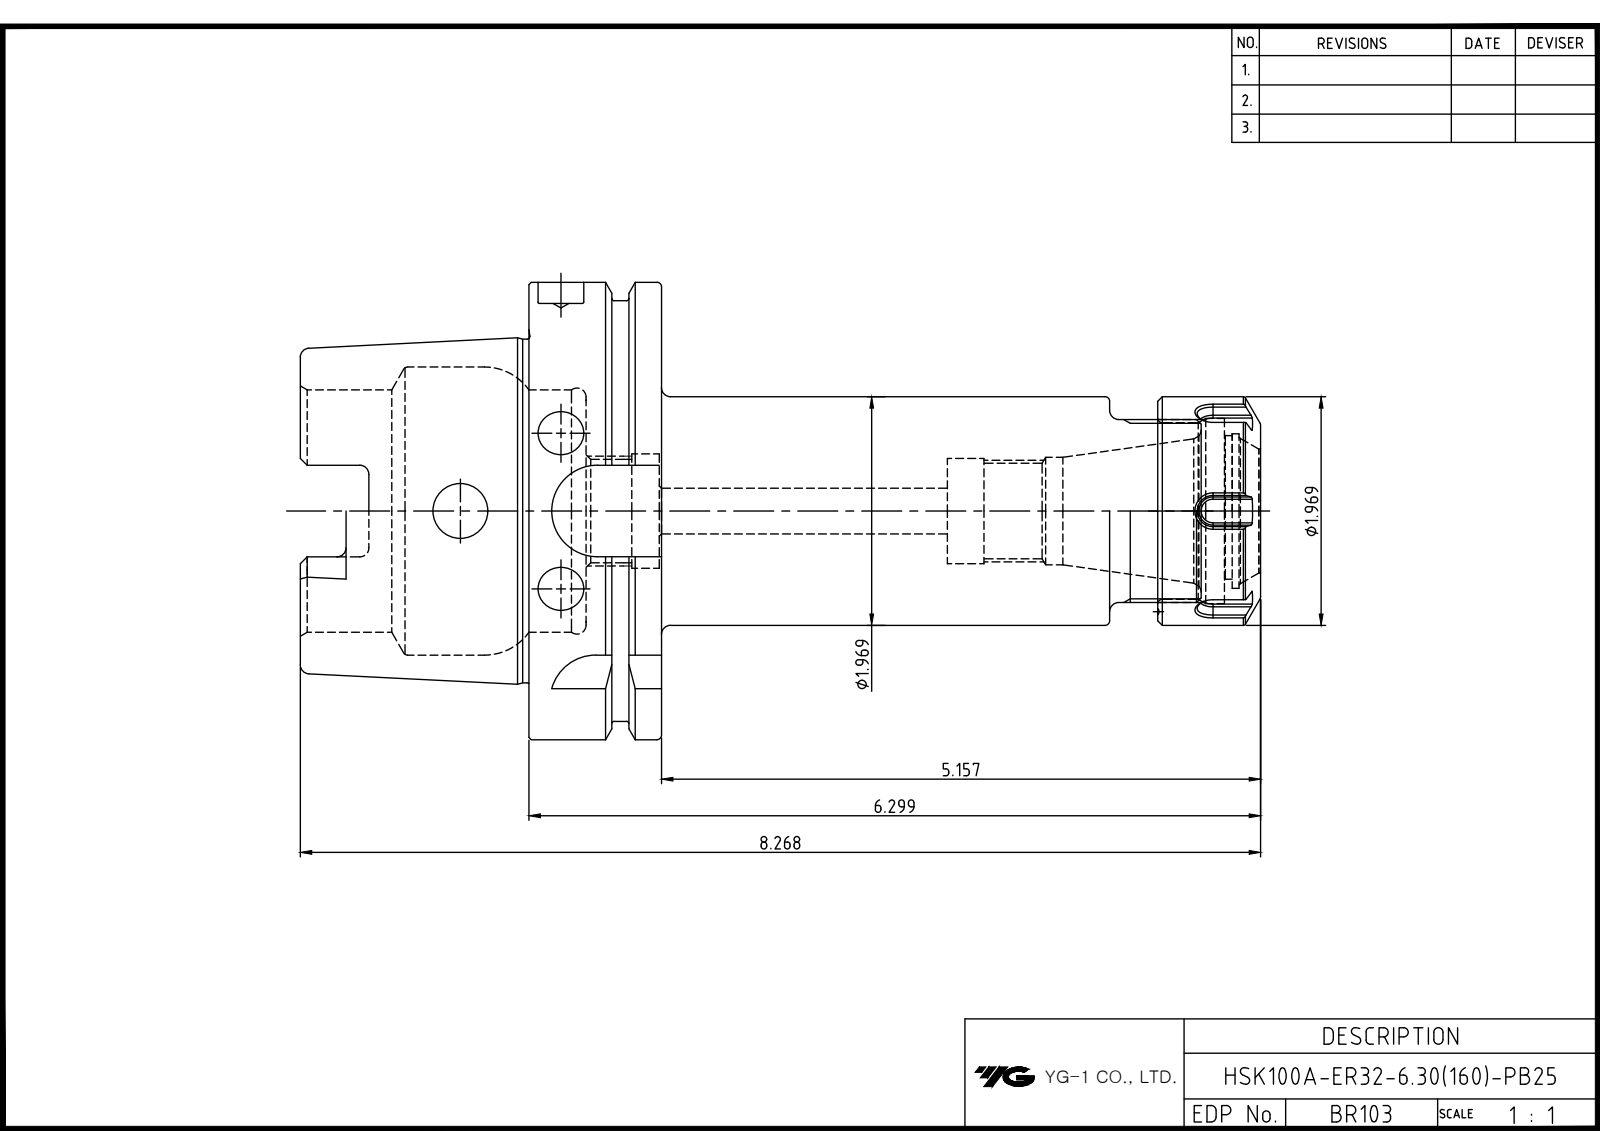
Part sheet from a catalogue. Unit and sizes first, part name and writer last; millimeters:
Units: millimetres
Overall size (bounding box): 210 × 100 × 100
Round holes (diameter × count): ⌀10 ×2, ⌀1 ×1, ⌀12 ×1, ⌀20.5 ×1, ⌀22.38 ×1, ⌀23 ×1, ⌀23.5 ×1, ⌀25 ×1, ⌀27.1 ×1, ⌀31.4 ×1, ⌀33.8 ×1, ⌀38.6 ×1
Round bosses / shafts (diameter × count): ⌀100 ×1, ⌀92 ×1, ⌀75.41 ×1, ⌀50 ×1, ⌀40 ×1
Partial cylindrical surfaces — rounded edges, fillets, slot ends (radius × count): R0.5 ×12, R2 ×6, R4.88 ×4, R10 ×4
Main face-to-face distances: 29, 12.5, 16.5, 62.5, 79, 50, 22.5, 137.5, 131.5, 210
Hole centre spacings: 0.8, 22, 22.8
Volume: 457 196 mm³ · Surface area: 81 967 mm²
Bodies: 2 solids, 204 faces (75 planar, 55 cylindrical, 74 other)
Part name (STEP PRODUCT): LO-HSK100A-ER32-6.30; ER32NUT
STEP written by: Autodesk Inventor 2025 (AUTOMOTIVE_DESIGN)
